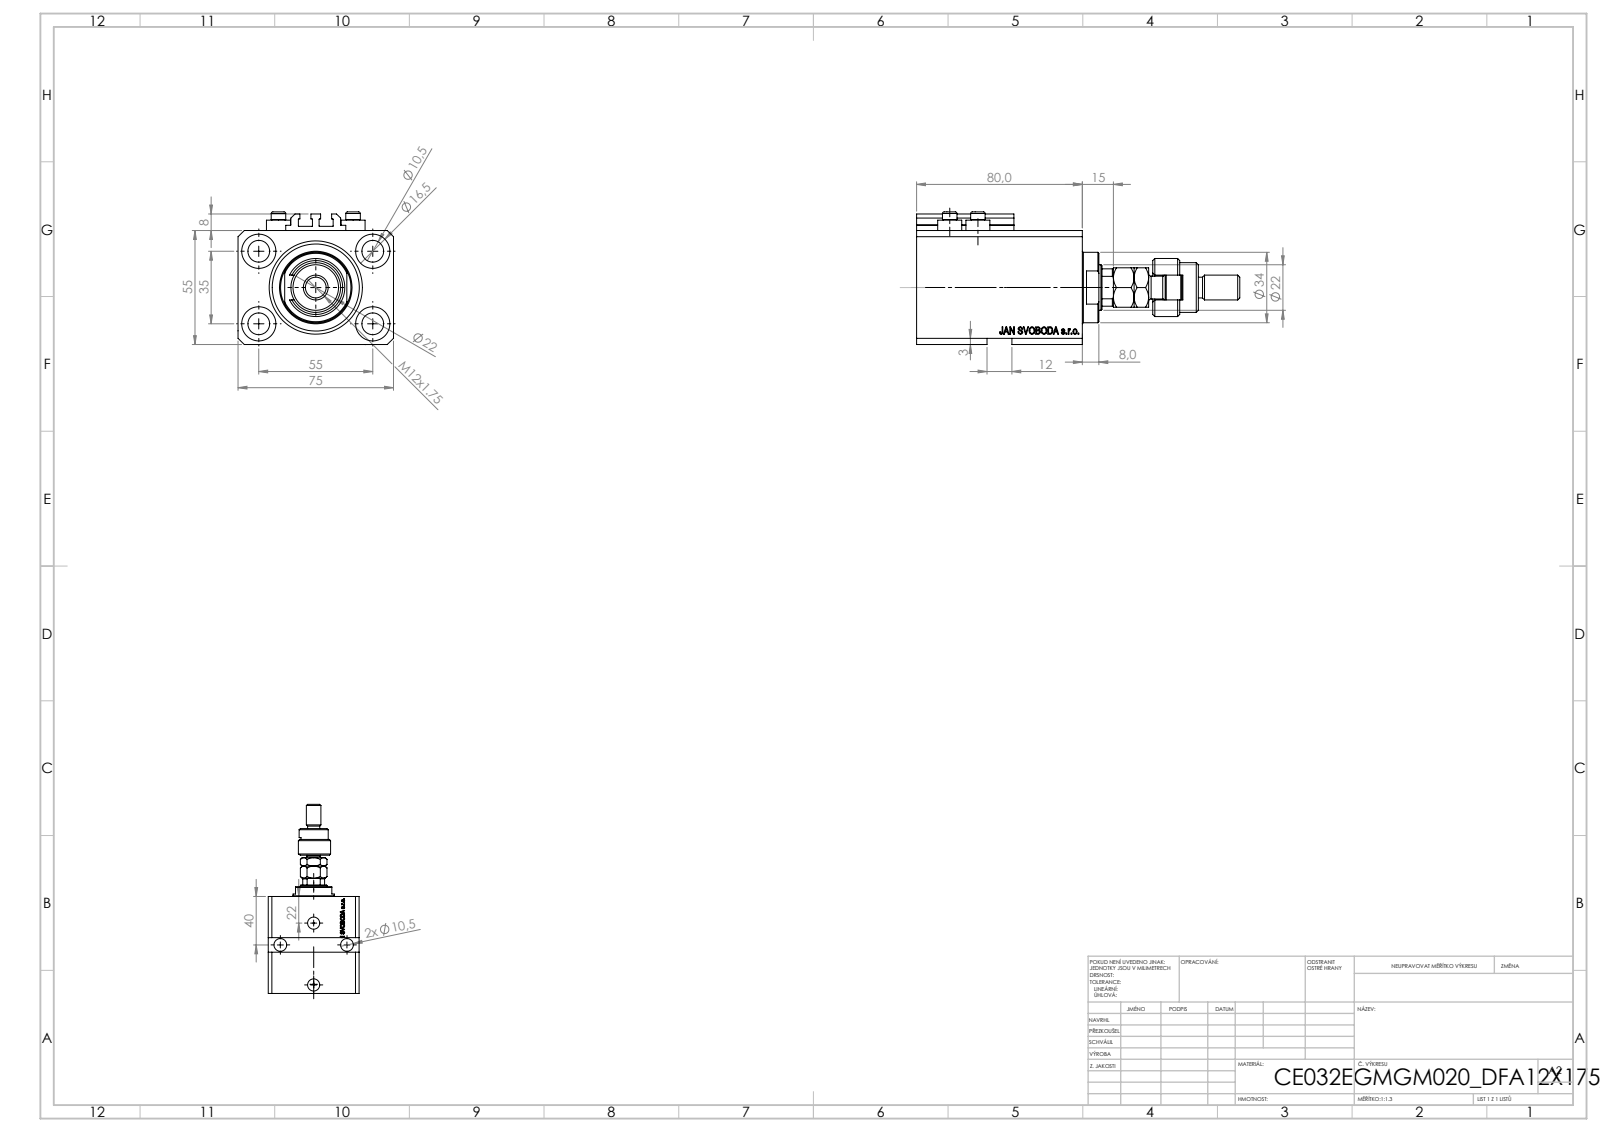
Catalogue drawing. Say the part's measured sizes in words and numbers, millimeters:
The part is named "ALLEN BOLT V250CE; V250CE_E_Body; V250CE_C_VCP; V250CE_VC_E (+2 more)". Its 3-D file was written by "SolidWorks 2019 (CONFIG_CONTROL_DESIGN)". It is 10 solids with 1149 faces: 542 planar, 139 cylindrical and 468 other. Overall it measures 156 by 75 by 64 millimeters. Its volume is 301 774 cubic millimeters and its surface area 81 585 square millimeters. Round holes: 7 of diameter 10.5, 4 of diameter 1.25, 4 of diameter 4, 4 of diameter 16.5, 2 of diameter 10, 2 of diameter 13.16, 2 of diameter 20, 1 of diameter 22, 1 of diameter 32, 1 of diameter 45. Round bosses or shafts: 4 of diameter 11.6, 4 of diameter 7, 1 of diameter 34, 1 of diameter 28, 1 of diameter 24, 1 of diameter 18, 1 of diameter 12, 1 of diameter 11. Partial cylindrical surfaces (rounded edges, fillets, slot ends): 10 of radius 0.2, 1 of radius 9.75, 1 of radius 10.5. The main face-to-face distances are 55, 75, 15, 80, 65, 3, 55.1, 9.9, 70.1, 8. The hole center spacings are 32.6, 55, 13.6, 14.09, 19.89, 20.12, 25.81, 28.48.
